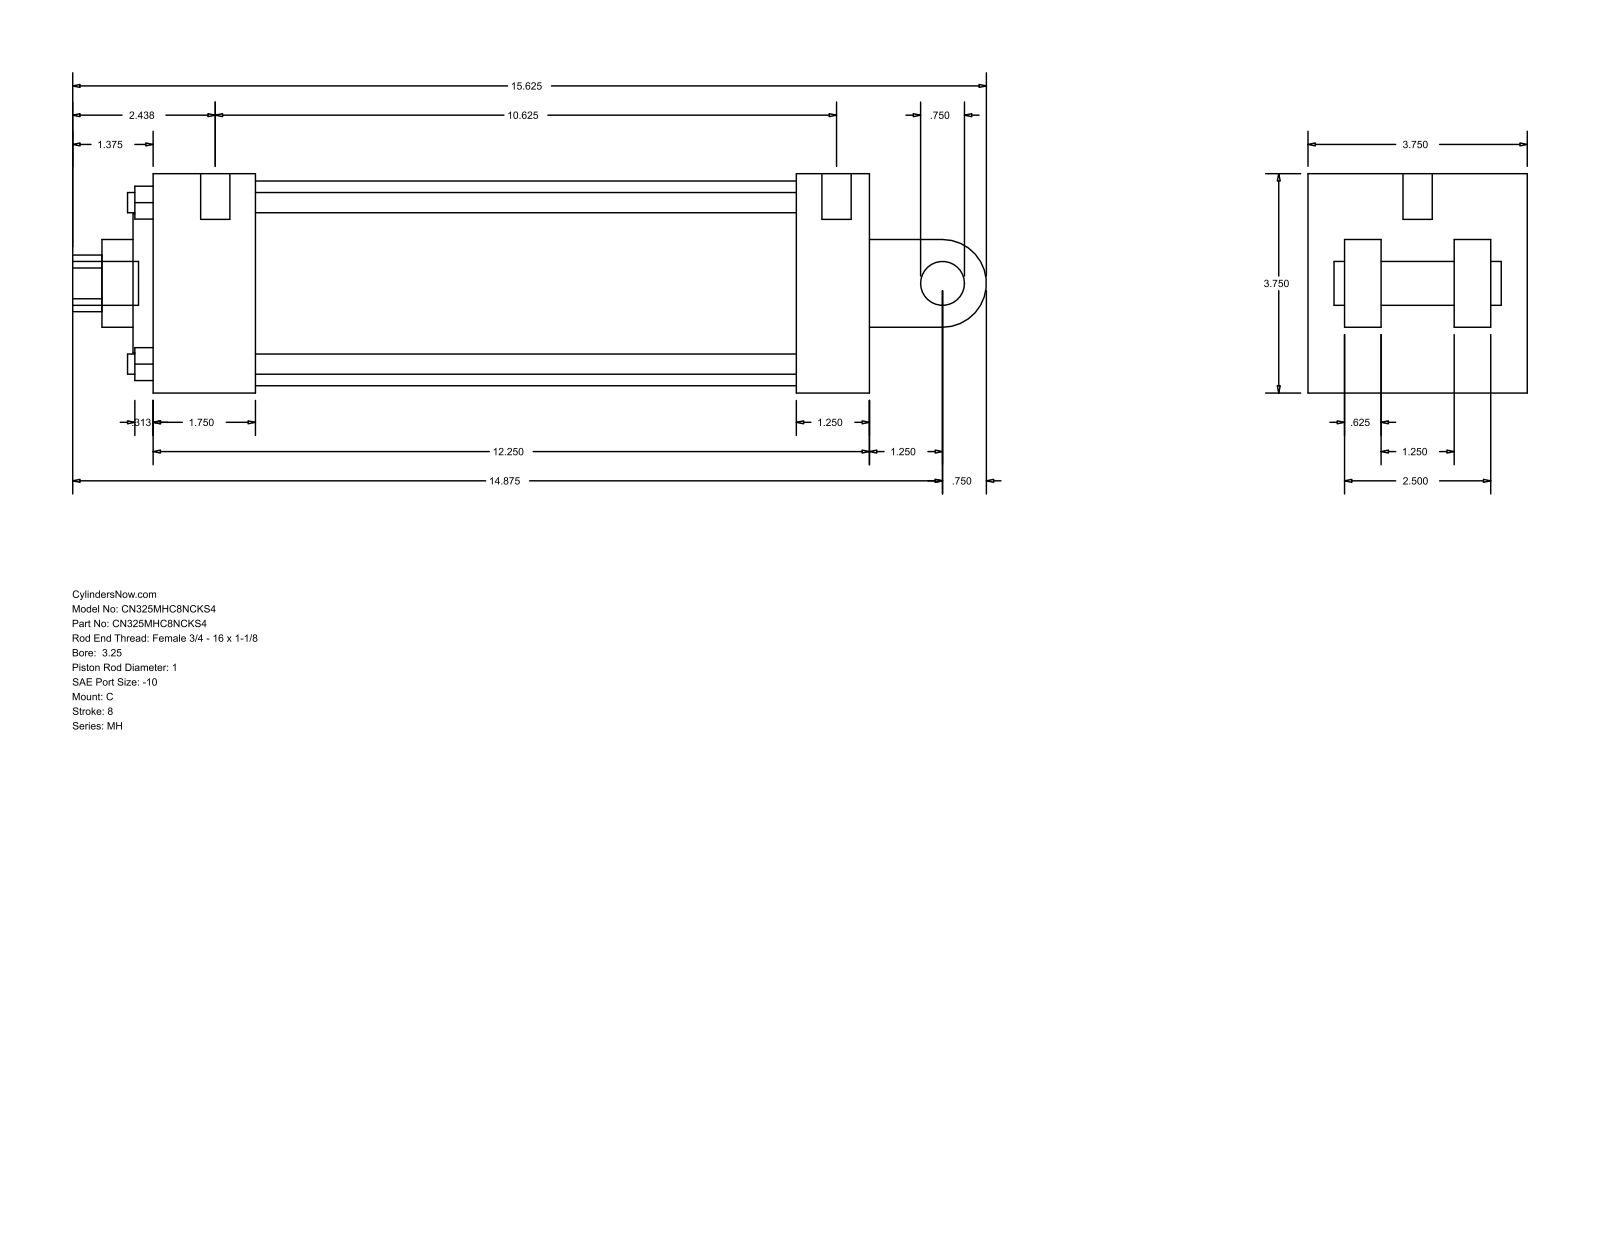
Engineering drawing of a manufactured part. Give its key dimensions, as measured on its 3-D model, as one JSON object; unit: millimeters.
{"part_name": "MH_C__0325_1", "step_written_by": "GSSL Pune (CONFIG_CONTROL_DESIGN)", "units": "millimeters", "bodies": {"solids": 0, "faces": 101, "planar": 71, "cylindrical": 30, "other": 0}, "overall_size": [396.88, 95.25, 95.25], "round_holes": [[8.76, 4], [5.56, 2], [12.7, 1], [25.4, 1], [38.1, 1], [60.33, 1], [88.9, 1]], "round_bosses_or_shafts": [[19.05, 2], [5.56, 2], [12.7, 1]], "partial_cylinders_radius": [[12.29, 1], [19.05, 1]], "face_to_face_distances": [95.24, 15.87, 311.15, 63.5, 79.37, 31.74, 47.63, 44.46, 279.4, 234.94], "hole_center_spacings": [49.57, 70.1, 99.14, 4.76]}
